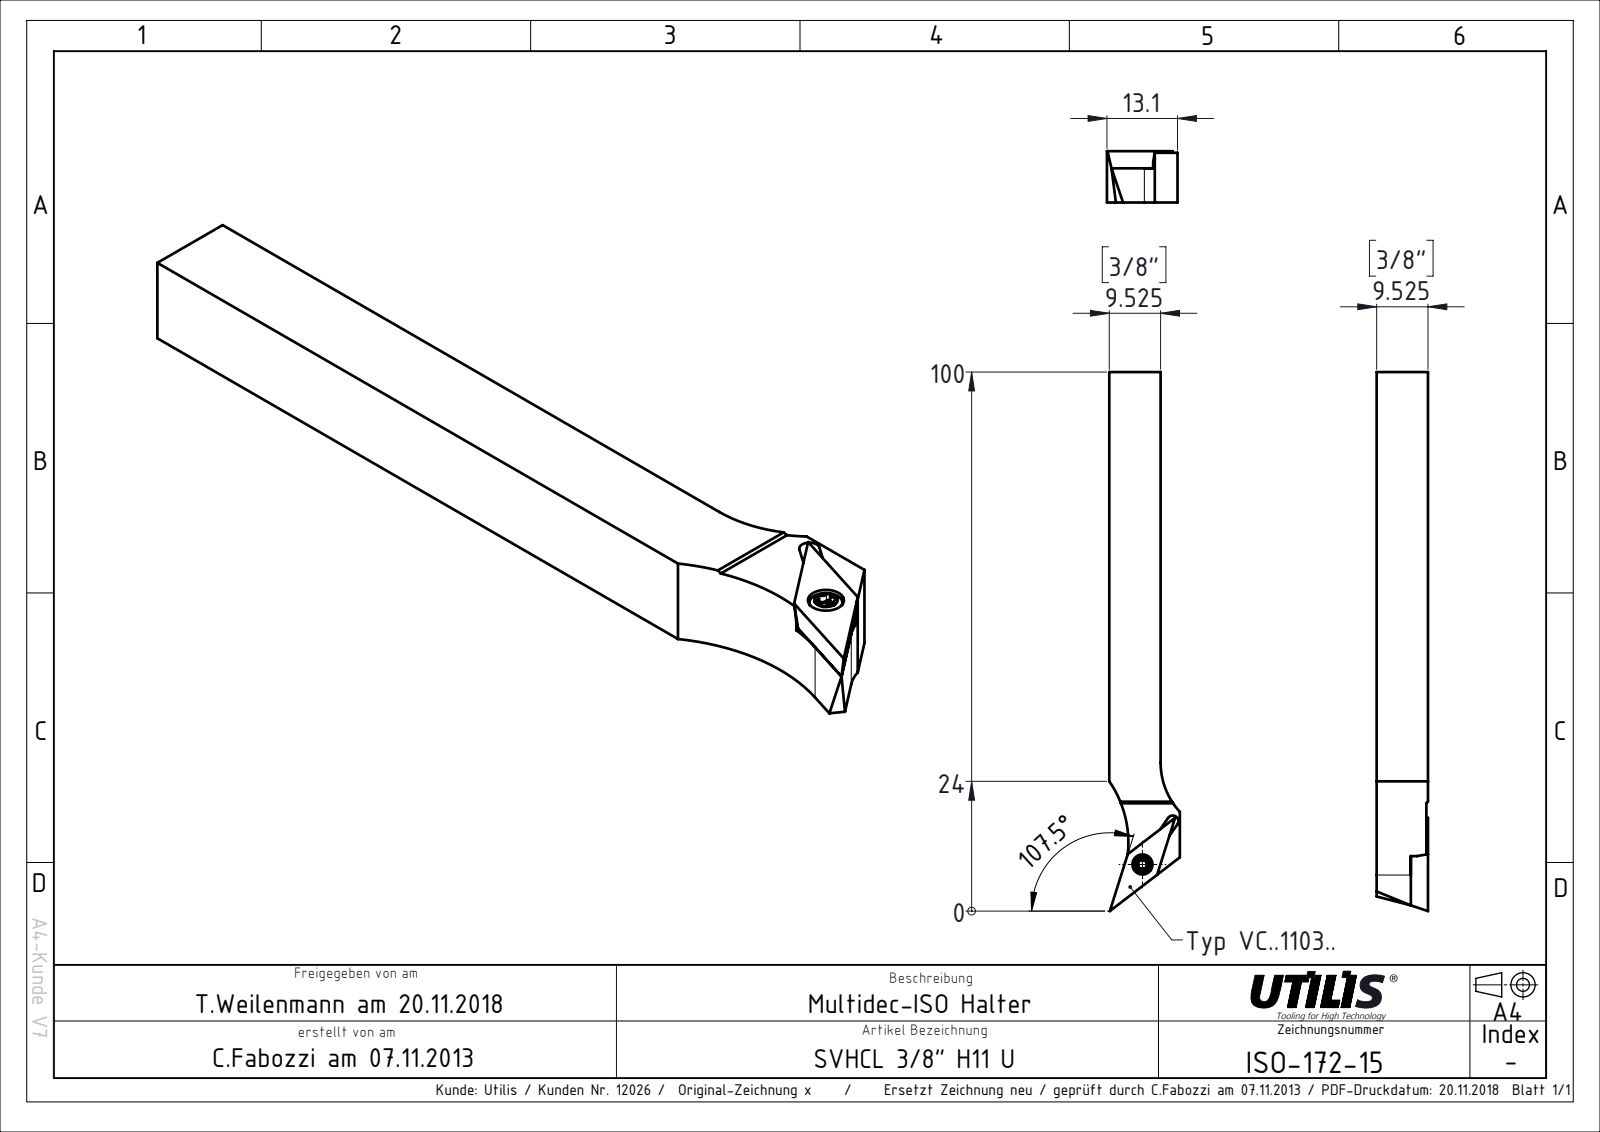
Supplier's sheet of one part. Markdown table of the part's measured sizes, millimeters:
| quantity | value |
| --- | --- |
| part name | MSP-7_M2,5X6-TX8 CERATIZIT Schraube; ISO-172_15; VCGT11; ISO-172-15 |
| STEP written by | SolidWorks 2017 (CONFIG_CONTROL_DESIGN) |
| units | millimeters |
| bodies | 3 solids, 82 faces (33 planar, 29 cylindrical, 20 other) |
| overall size | 100 × 13.1 × 9.53 |
| volume | 8 541 mm³ |
| surface area | 4 220 mm² |
| round holes (diameter × count) | 1.65 × 1, 2.05 × 1, 3.1 × 1 |
| round bosses / shafts (diameter × count) | 3.4 × 1, 2.5 × 1 |
| partial cylindrical surfaces (radius × count) | 0.2 × 6, 0.45 × 6, 1.05 × 1, 6.1 × 1, 13.5 × 1, 20 × 1 |
| main face-to-face distances | 9.53, 6.35, 3.18, 13.1, 3.57, 9.23, 2.88, 0.39, 6.32, 5.93 |
